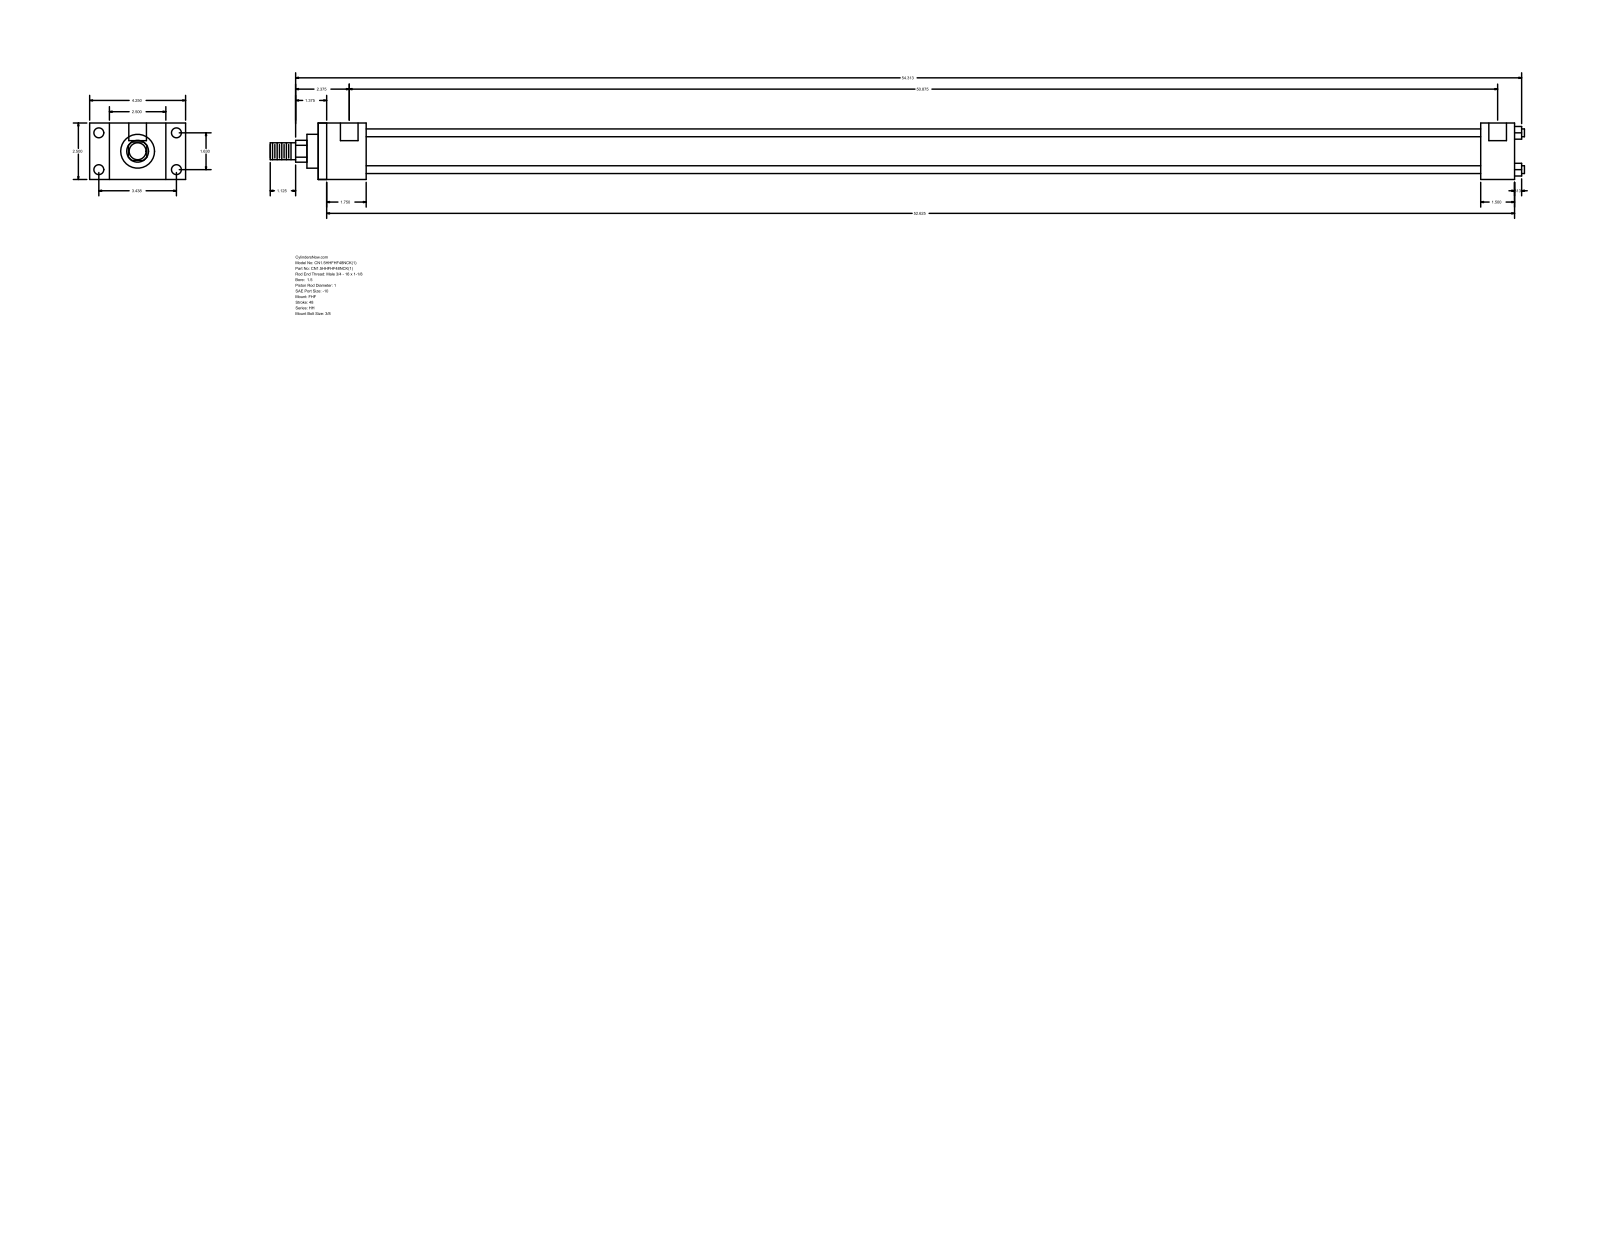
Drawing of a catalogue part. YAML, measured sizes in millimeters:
part_name: "HH_FHF__0150_1"
step_written_by: "GSSL Pune (CONFIG_CONTROL_DESIGN)"
units: millimeters
bodies: {solids: 0, faces: 88, planar: 60, cylindrical: 28, other: 0}
overall_size: [1411.29, 107.95, 63.5]
round_holes:
  - {diameter: 5.56, count: 4}
  - {diameter: 11.13, count: 4}
  - {diameter: 19.84, count: 2}
round_bosses_or_shafts:
  - {diameter: 8.76, count: 4}
  - {diameter: 44.45, count: 1}
  - {diameter: 38.1, count: 1}
  - {diameter: 25.4, count: 1}
  - {diameter: 19.05, count: 1}
partial_cylinders:
  - {radius: 12.29, count: 1}
face_to_face_distances: [63.5, 22.23, 85.73, 53.98, 107.96, 1346.2, 1292.22, 38.1, 1308.1, 1254.12]
hole_center_spacings: [1.59, 41.4, 87.32, 96.64, 1293.81, 1295.4, 1292.22]
